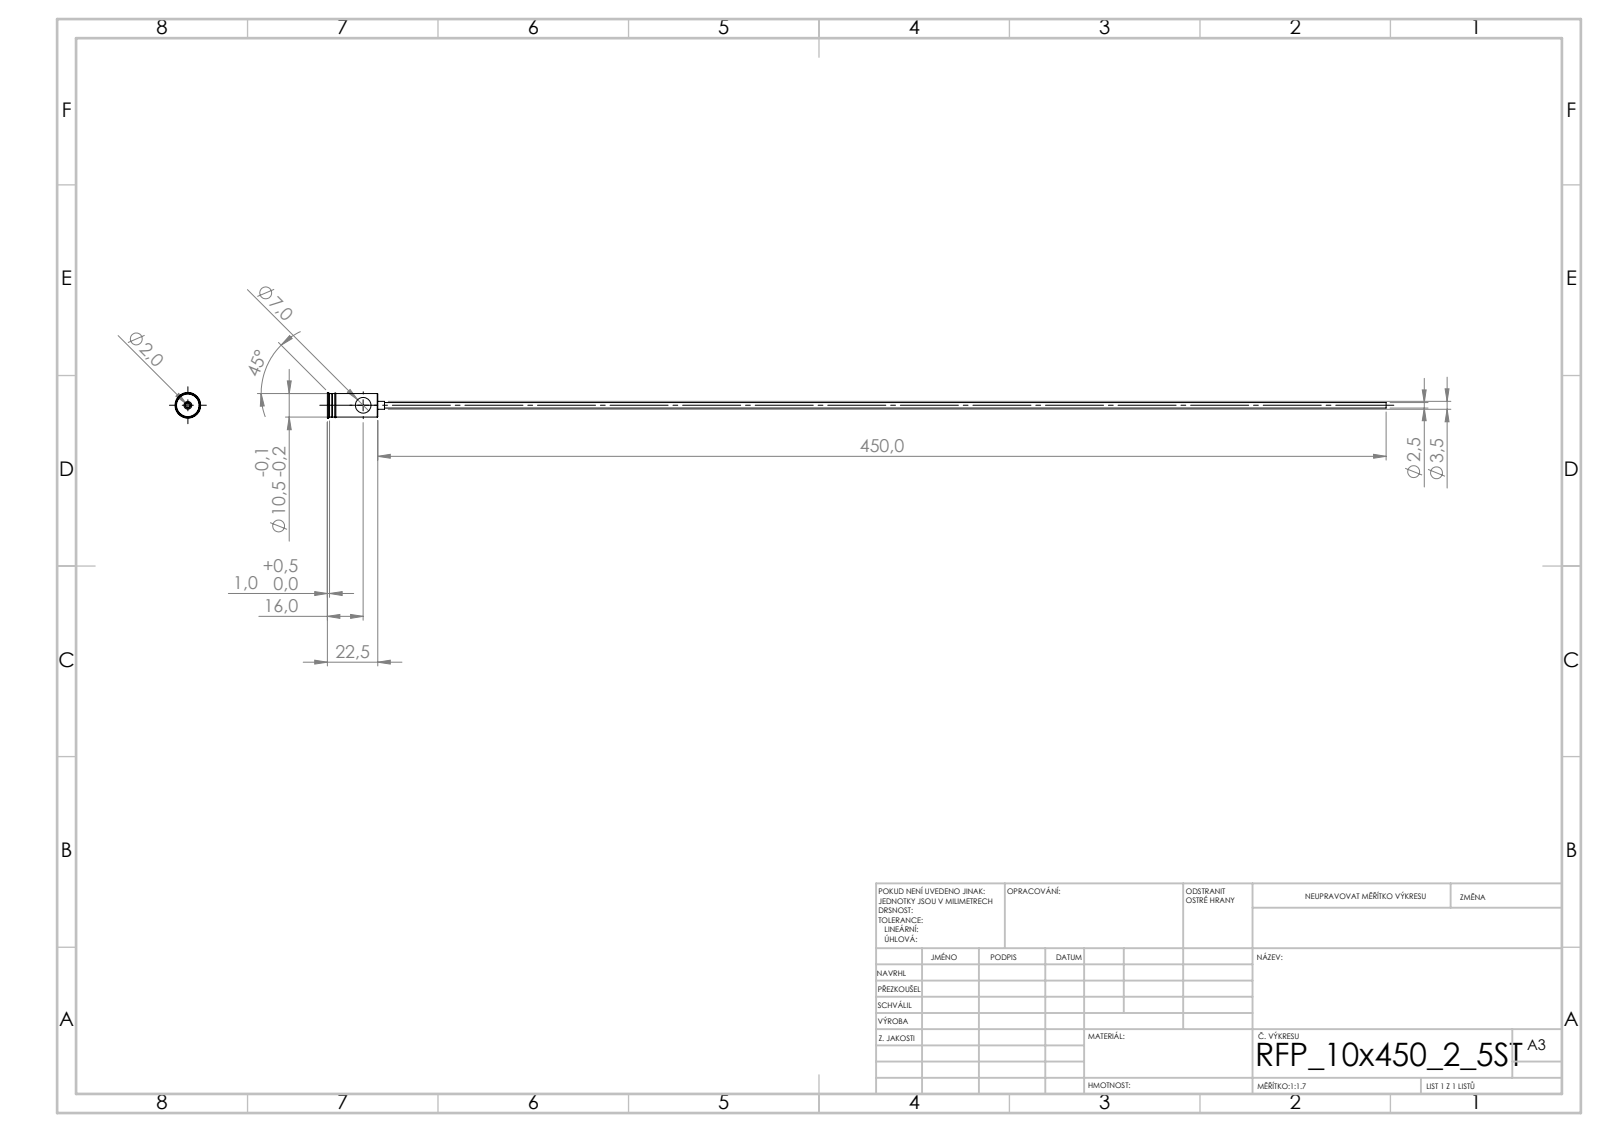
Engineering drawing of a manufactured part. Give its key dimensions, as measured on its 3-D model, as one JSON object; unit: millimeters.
{"step_written_by": "SolidWorks 2019 (CONFIG_CONTROL_DESIGN)", "units": "millimeters", "bodies": {"solids": 1, "faces": 44, "planar": 20, "cylindrical": 16, "other": 8}, "overall_size": [472.5, 11.5, 11.5], "volume_mm3": 2322, "surface_area_mm2": 7508, "round_holes": [[2, 1], [7, 1]], "round_bosses_or_shafts": [[11.5, 1], [10.5, 1], [3.5, 1], [2.5, 1]], "face_to_face_distances": [22.5, 20.5, 2, 5.9, 20.2, 2.3, 3, 23.2, 23.5, 25.5]}
